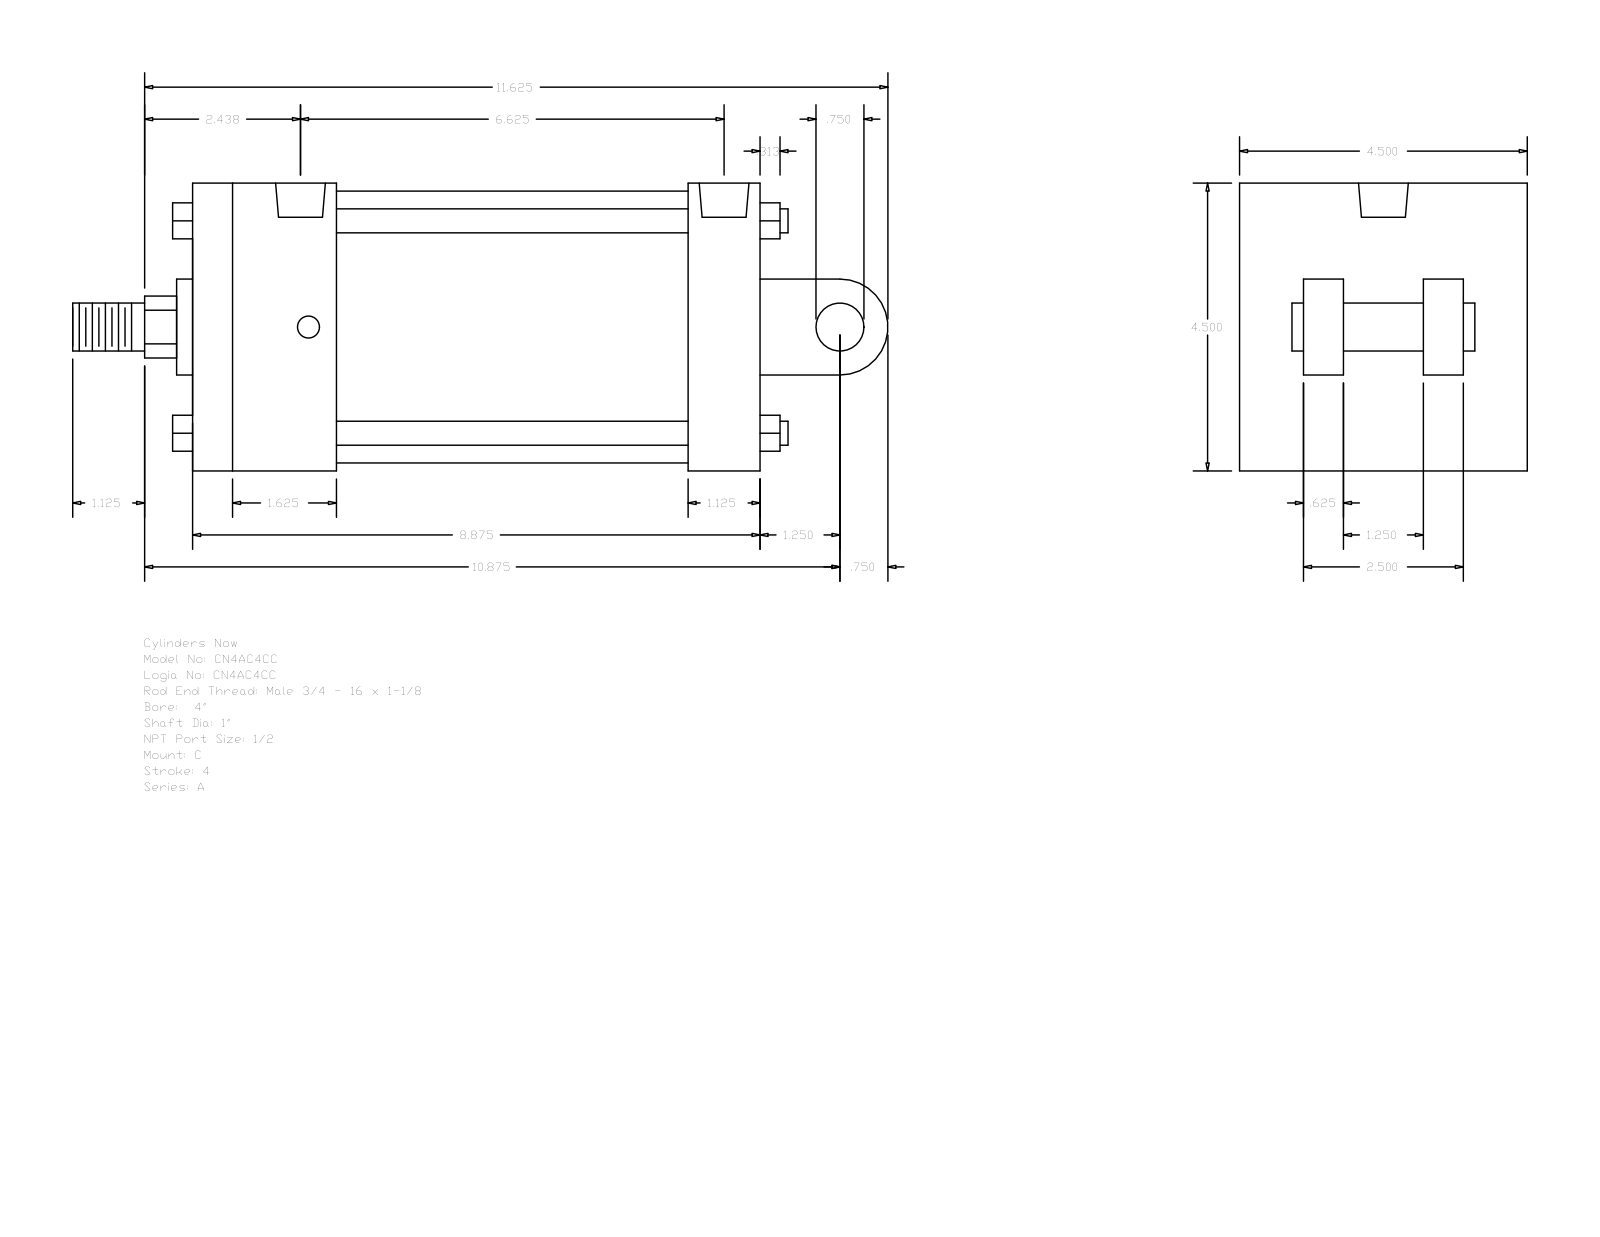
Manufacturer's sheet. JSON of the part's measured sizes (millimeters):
{"part_name": "A_C__0400_1", "step_written_by": "GSSL Pune (CONFIG_CONTROL_DESIGN)", "units": "millimeters", "bodies": {"solids": 0, "faces": 135, "planar": 102, "cylindrical": 33, "other": 0}, "overall_size": [323.85, 114.3, 114.3], "round_holes": [[8.73, 4], [19.77, 2]], "round_bosses_or_shafts": [[9.53, 4], [19.05, 2], [107.95, 1], [38.1, 1], [25.4, 1]], "partial_cylinders_radius": [[12.29, 1], [19.05, 1]], "face_to_face_distances": [114.3, 225.42, 73.03, 28.57, 196.85, 57.15, 139.7, 168.27, 41.27, 38.1], "hole_center_spacings": [3.18, 161.92, 165.1, 168.28]}
